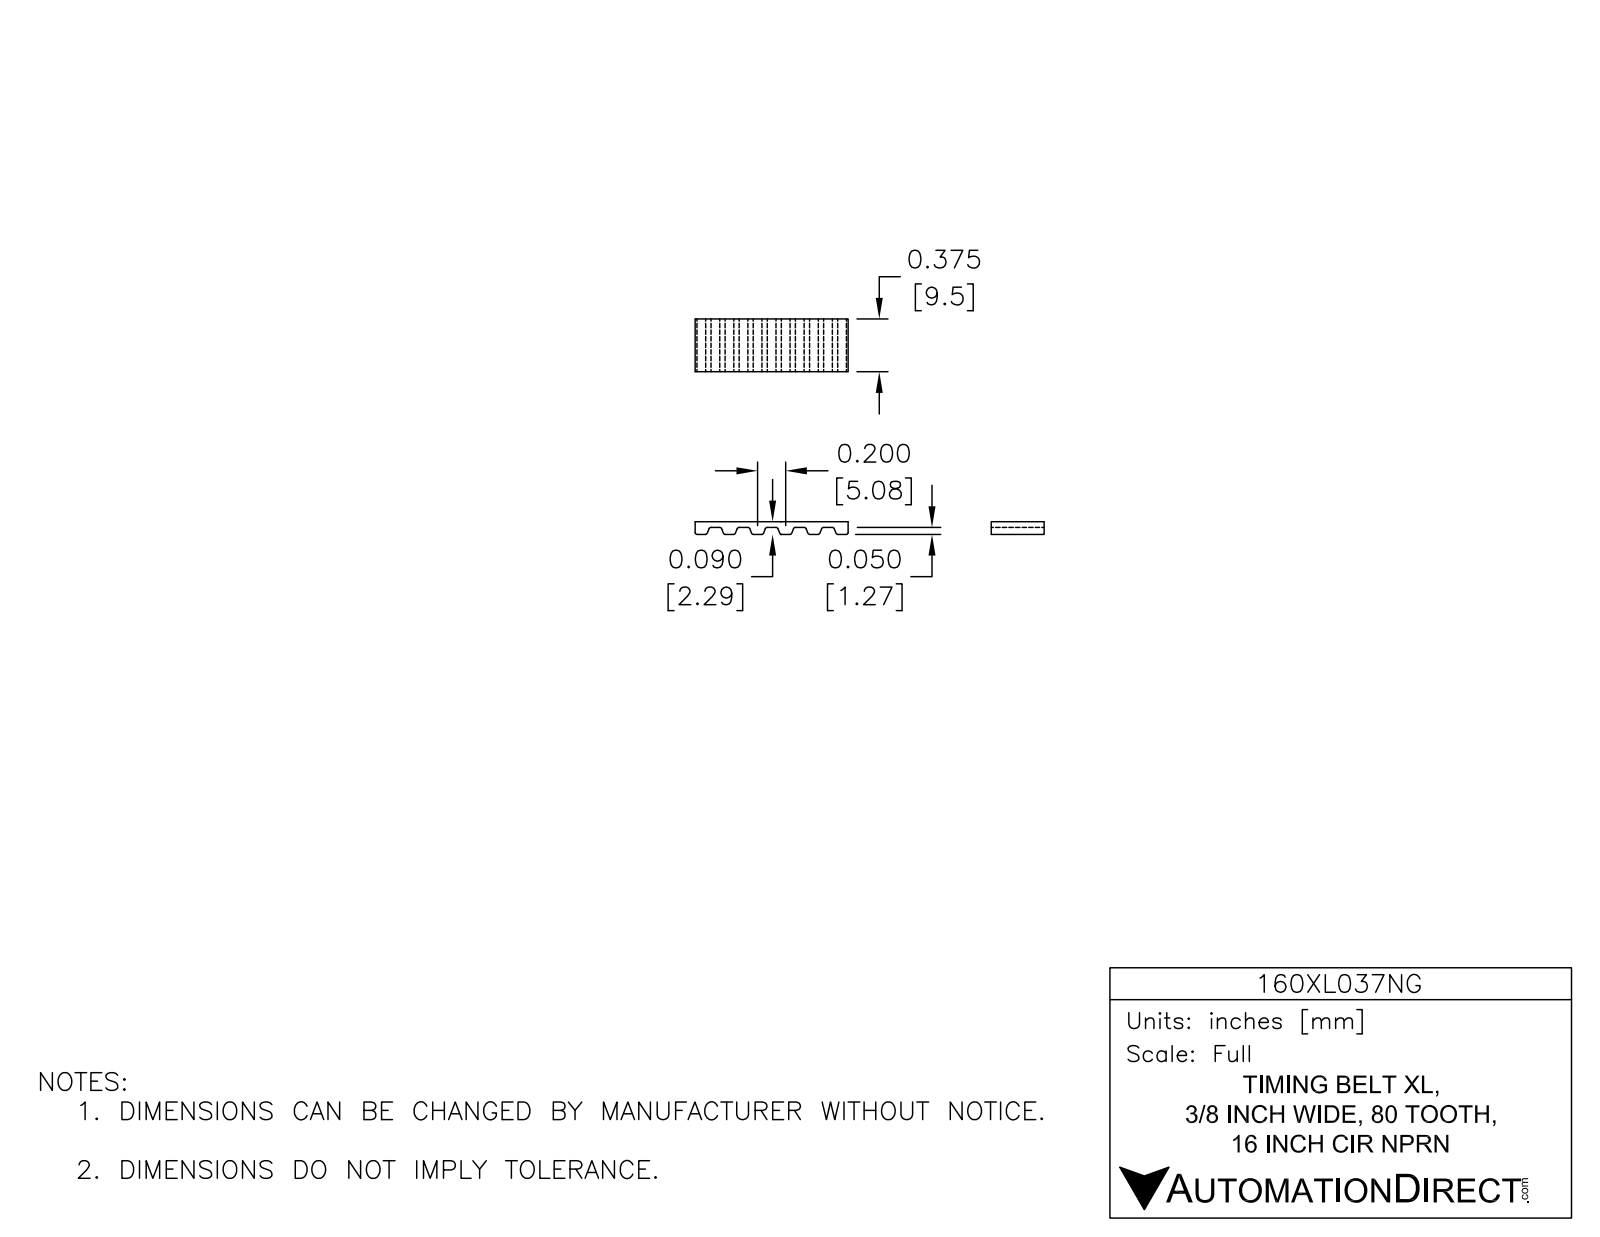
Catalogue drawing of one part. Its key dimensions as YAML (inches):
part_name: "160XL037NG"
step_written_by: "SolidWorks 2014 (AUTOMOTIVE_DESIGN)"
units: inches
bodies: {solids: 1, faces: 678, planar: 280, cylindrical: 398, other: 0}
overall_size: [6.288, 3, 0.375]
volume: 0.326
surface_area: 15.3
partial_cylinders:
  - {radius: 0.015, count: 320}
  - {radius: 1.46, count: 2}
  - {radius: 1.5, count: 2}
face_to_face_distances: [3, 0.04, 2.96, 0.375, 2.92, 0.178, 0.357, 0.535, 0.713, 0.892]
